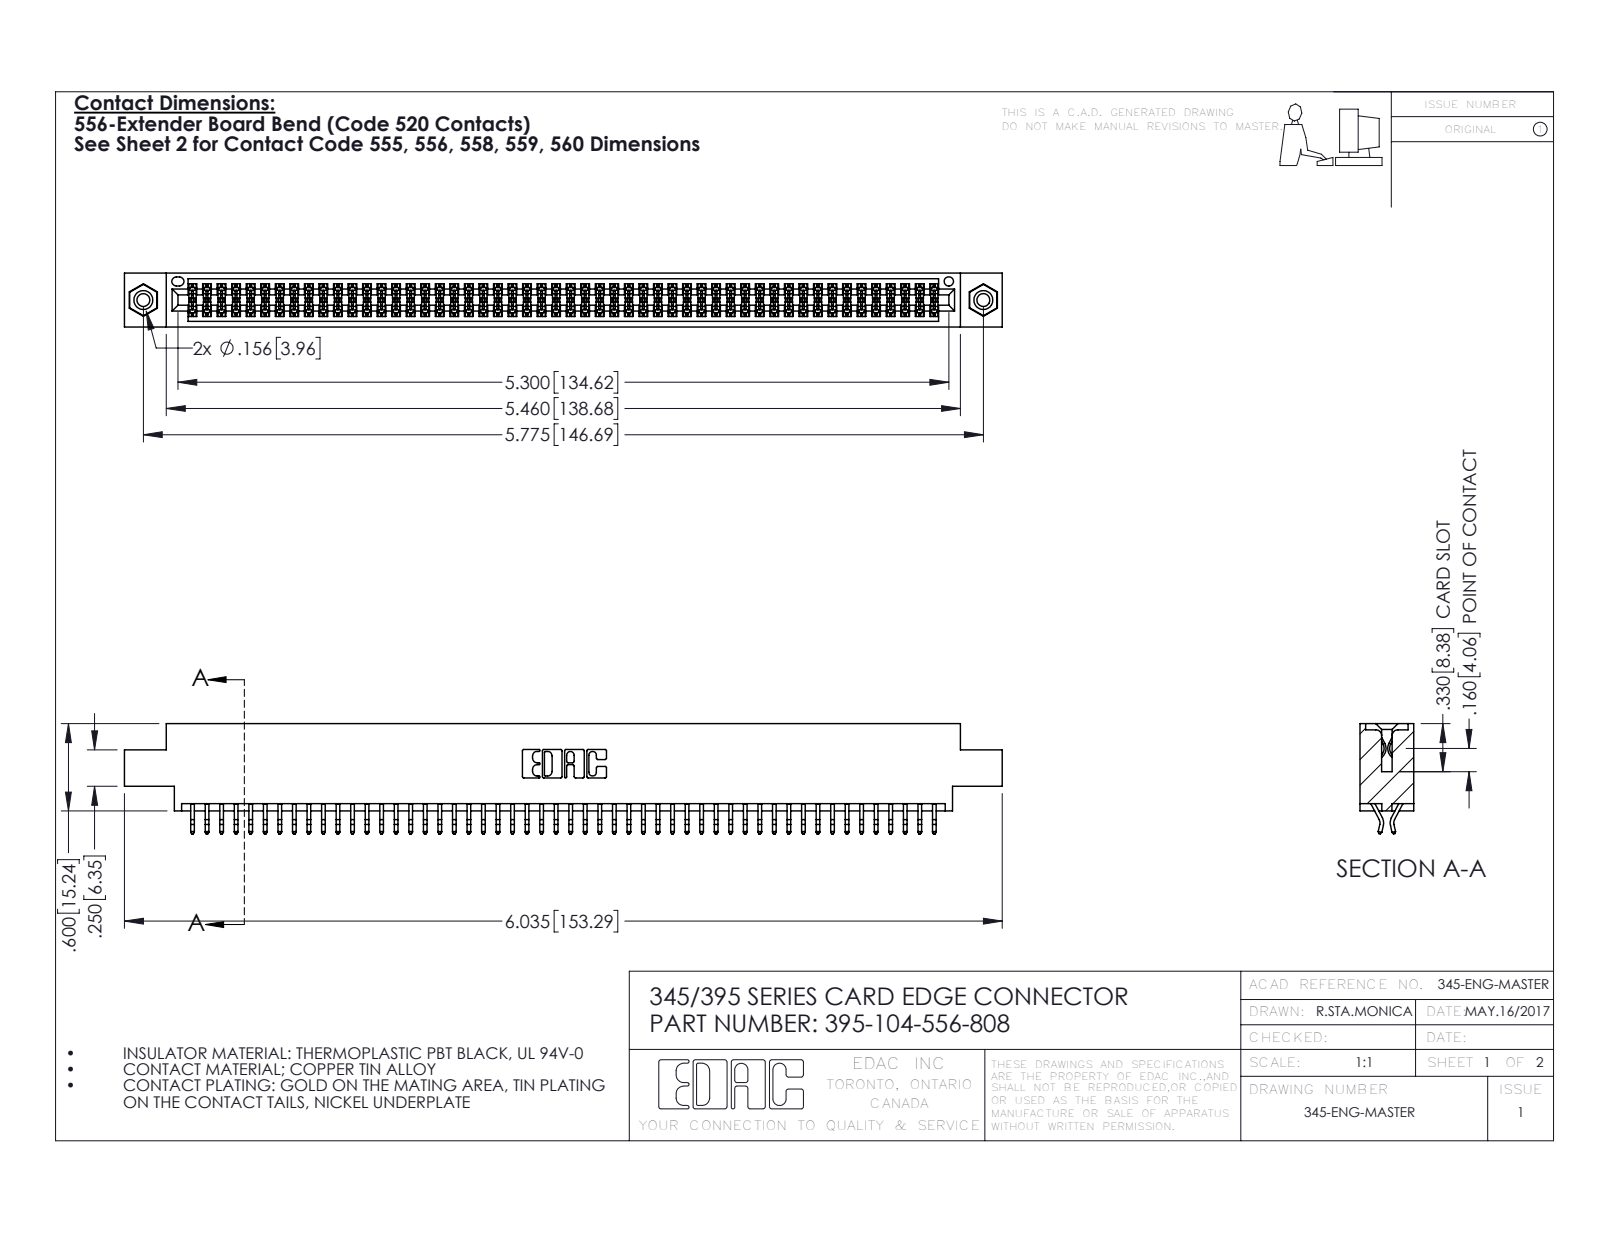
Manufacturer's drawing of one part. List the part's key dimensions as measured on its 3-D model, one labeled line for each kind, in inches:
Part name (STEP PRODUCT): 395-104-556-808; 345-292-001_556 Tail; 345-250-001_345-250-003-102; 345 Part_0.170 Offset - 0.156 Dia-TI
STEP written by: SolidWorks 2016 (CONFIG_CONTROL_DESIGN)
Units: inches
Bodies: 107 solids, 6014 faces (3964 planar, 2034 cylindrical, 16 other)
Overall size (bounding box): 6.035 × 0.757 × 0.37
Volume: 0.907 in³ · Surface area: 34.45 in²
Round holes (diameter × count): ⌀0.089 ×2, ⌀0.125 ×2, ⌀0.156 ×2, ⌀0.064 ×1
Round bosses / shafts (diameter × count): ⌀0.155 ×2
Partial cylindrical surfaces — rounded edges, fillets, slot ends (radius × count): R0.006 ×156, R0.01 ×22, R0.007 ×6, R0.031 ×6, R0.026 ×3, R0.01 ×2, R0.014 ×2, R0.019 ×2
Main face-to-face distances: 0.072, 0.298, 0.37, 0.2, 0.025, 0.098, 0.272, 0.225, 0.175, 0.149
Hole centre spacings: 0.27, 5.539, 5.775
